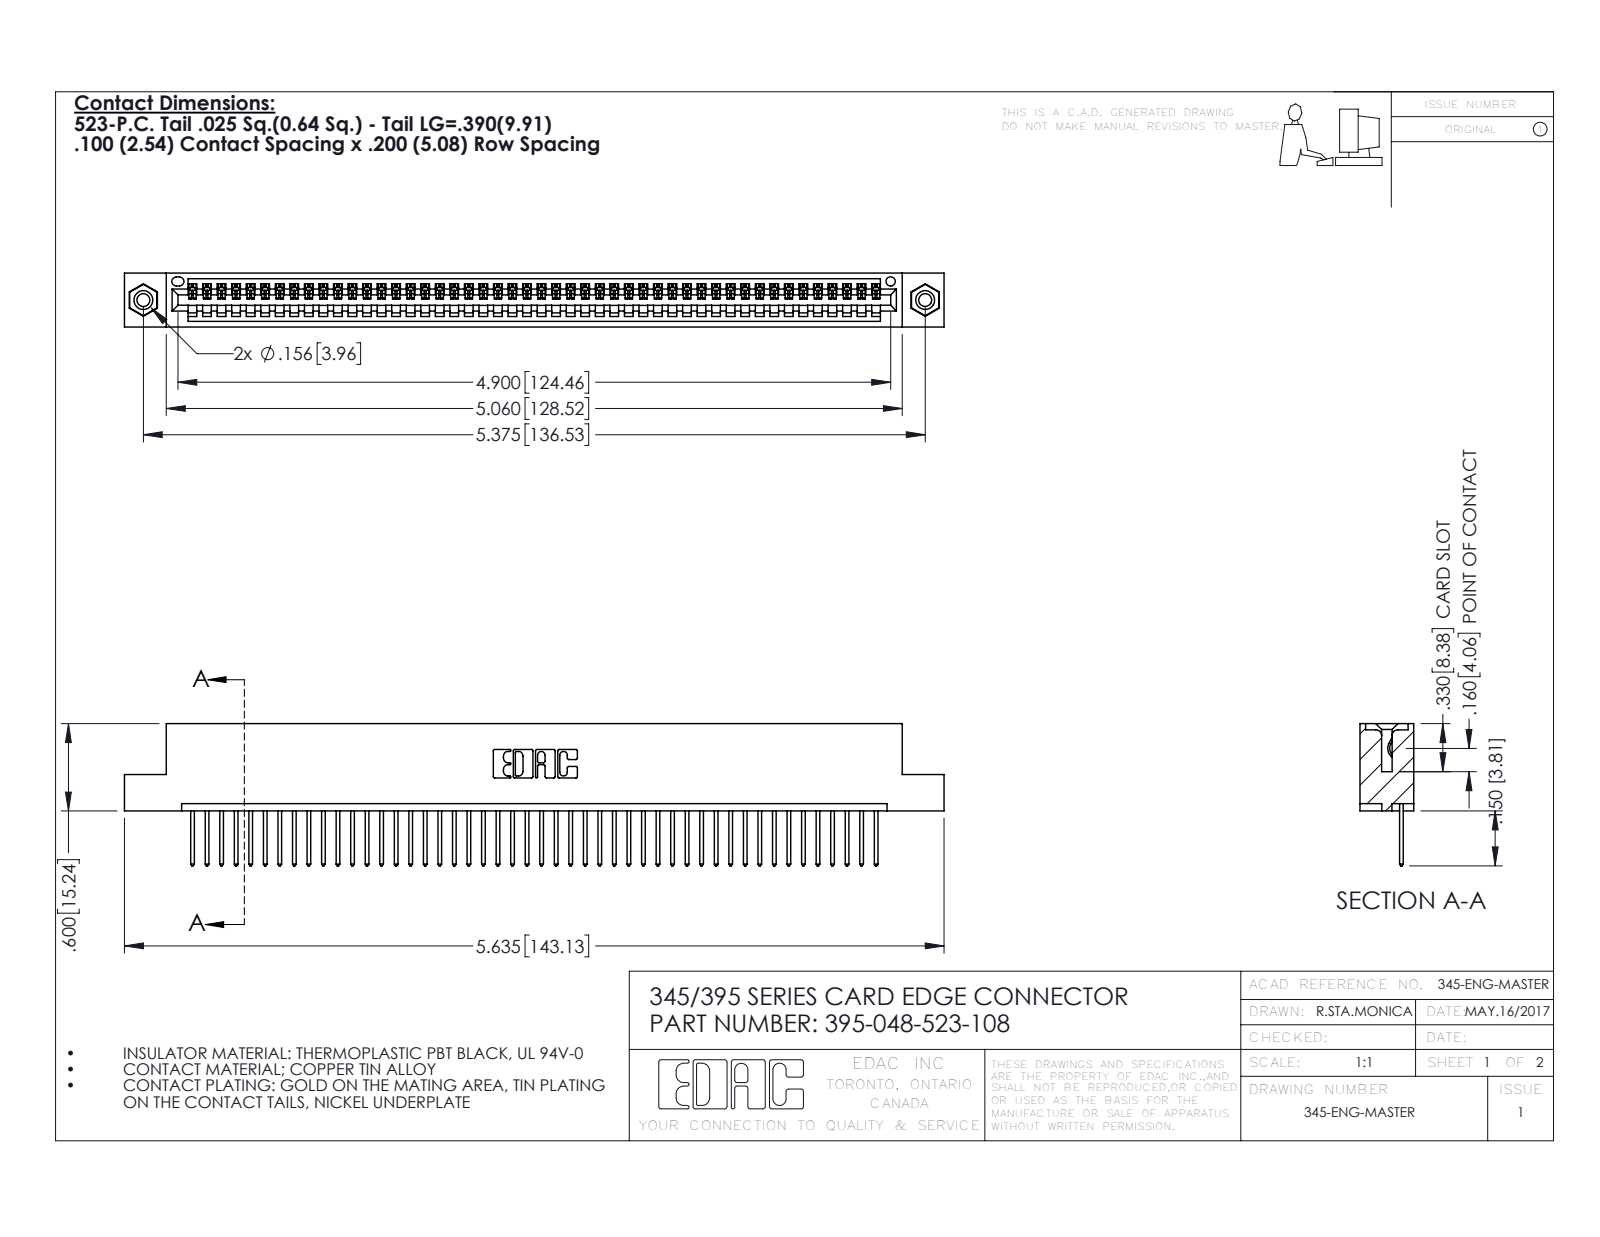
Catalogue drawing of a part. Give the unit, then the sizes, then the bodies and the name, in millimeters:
Units: millimetres
Overall size (bounding box): 143.1 × 24.8 × 9.4
Round holes (diameter × count): ⌀2.3 ×2, ⌀3.2 ×2, ⌀4 ×2, ⌀1.6 ×1
Round bosses / shafts (diameter × count): ⌀3.9 ×2
Partial cylindrical surfaces — rounded edges, fillets, slot ends (radius × count): R0.2 ×96, R0.3 ×96, R0.3 ×22, R0.2 ×6, R0.8 ×6, R0.7 ×3, R0.8 ×2, R1 ×2
Main face-to-face distances: 1.8, 7.6, 9.4, 5.1, 2.5, 6.9, 0.6, 5.7, 3.8, 1.8
Hole centre spacings: 6.9, 130.5, 136.5
Volume: 13 600 mm³ · Surface area: 18 250 mm²
Bodies: 51 solids, 2970 faces (2032 planar, 922 cylindrical, 16 other)
Part name (STEP PRODUCT): 345-292-001_345-293-123; 345-250-001_345-250-003-102; 395-048-523-108; 345 Part_Flush Mounting Lugs - 0.156 Dia-TI
STEP written by: SolidWorks 2016 (CONFIG_CONTROL_DESIGN)
